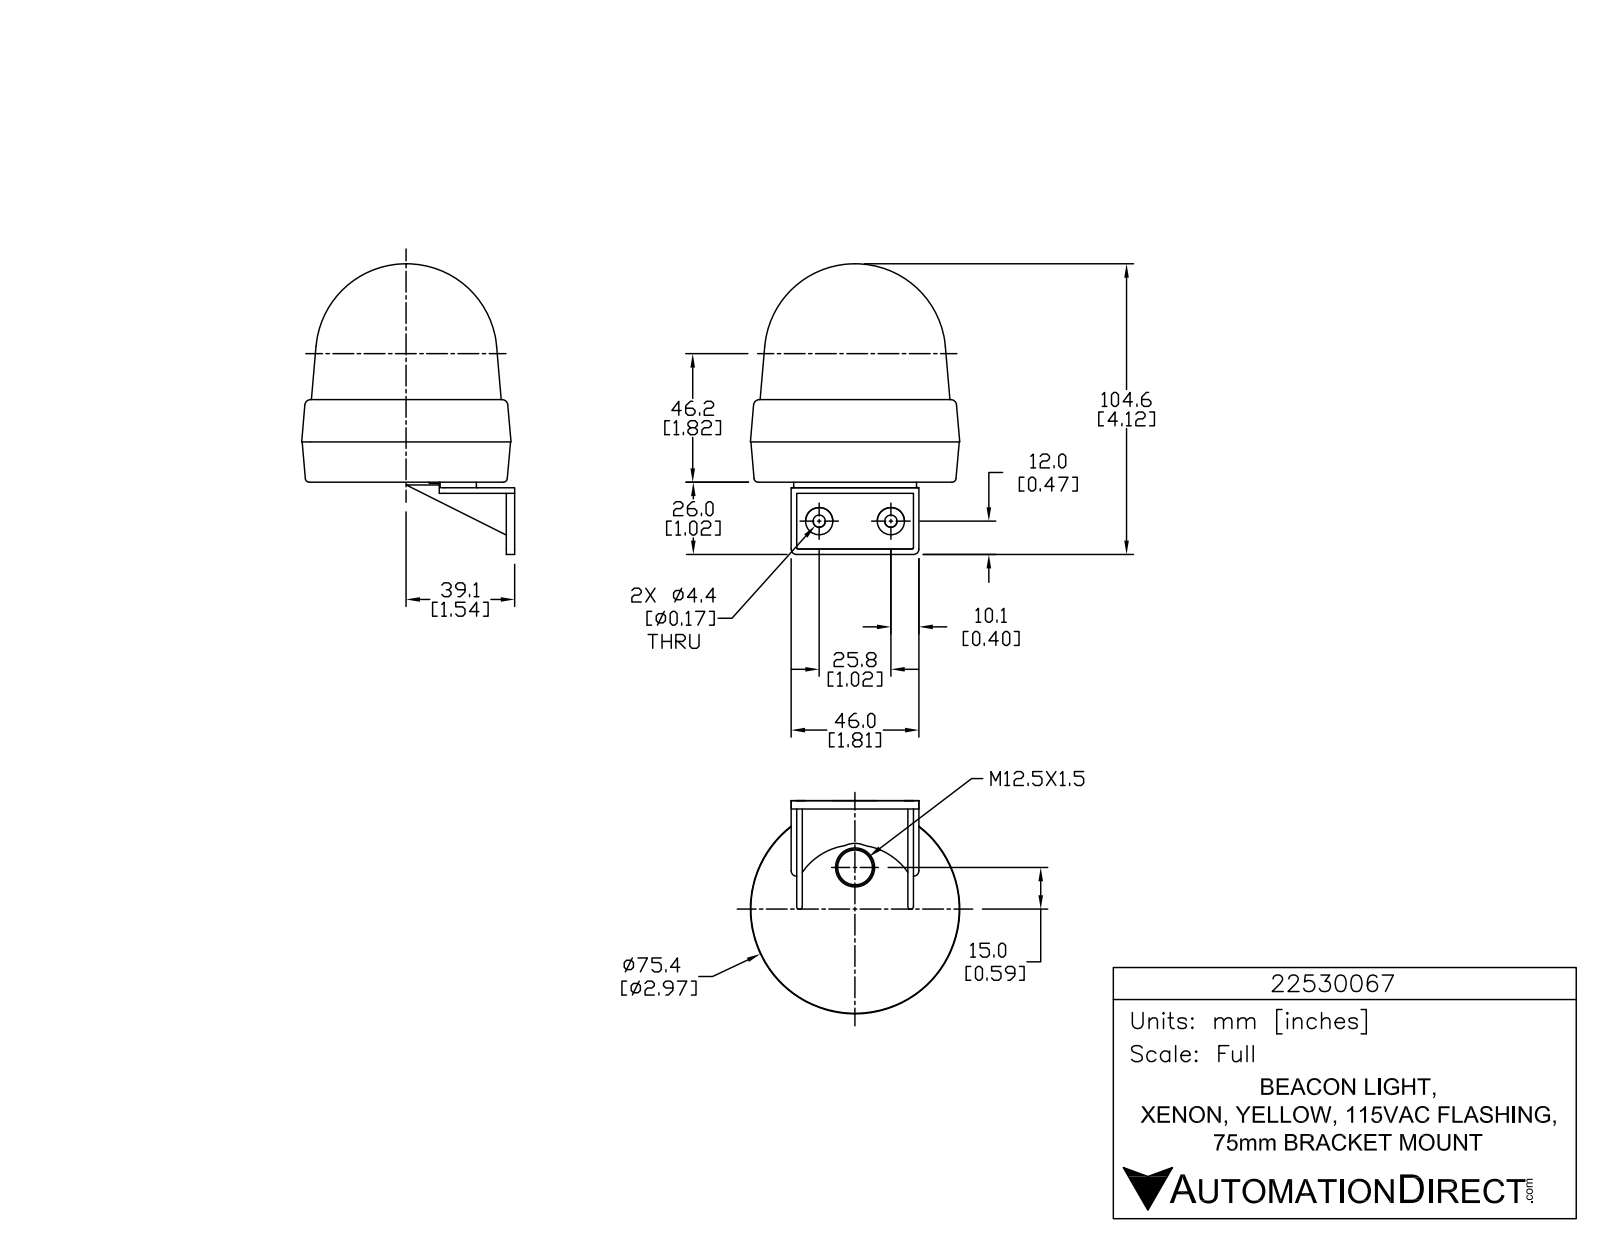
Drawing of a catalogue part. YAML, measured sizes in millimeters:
part_name: "22530067"
step_written_by: "SolidWorks 2015 (AUTOMOTIVE_DESIGN)"
units: millimeters
bodies: {solids: 1, faces: 819, planar: 549, cylindrical: 180, other: 90}
overall_size: [104.6, 82.6, 75.4]
volume: 262500
surface_area: 27080
round_holes:
  - {diameter: 1.5, count: 3}
  - {diameter: 4.4, count: 2}
round_bosses_or_shafts:
  - {diameter: 8.6, count: 3}
  - {diameter: 2.1, count: 3}
  - {diameter: 9.8, count: 2}
partial_cylinders:
  - {radius: 0.1, count: 9}
  - {radius: 0.1, count: 6}
  - {radius: 0.3, count: 6}
  - {radius: 0.3, count: 6}
  - {radius: 0.3, count: 6}
  - {radius: 0.5, count: 6}
  - {radius: 5, count: 6}
  - {radius: 2, count: 4}
face_to_face_distances: [2, 4, 40, 1, 3, 42, 38, 2, 42, 44]
hole_center_spacings: [25.8]
